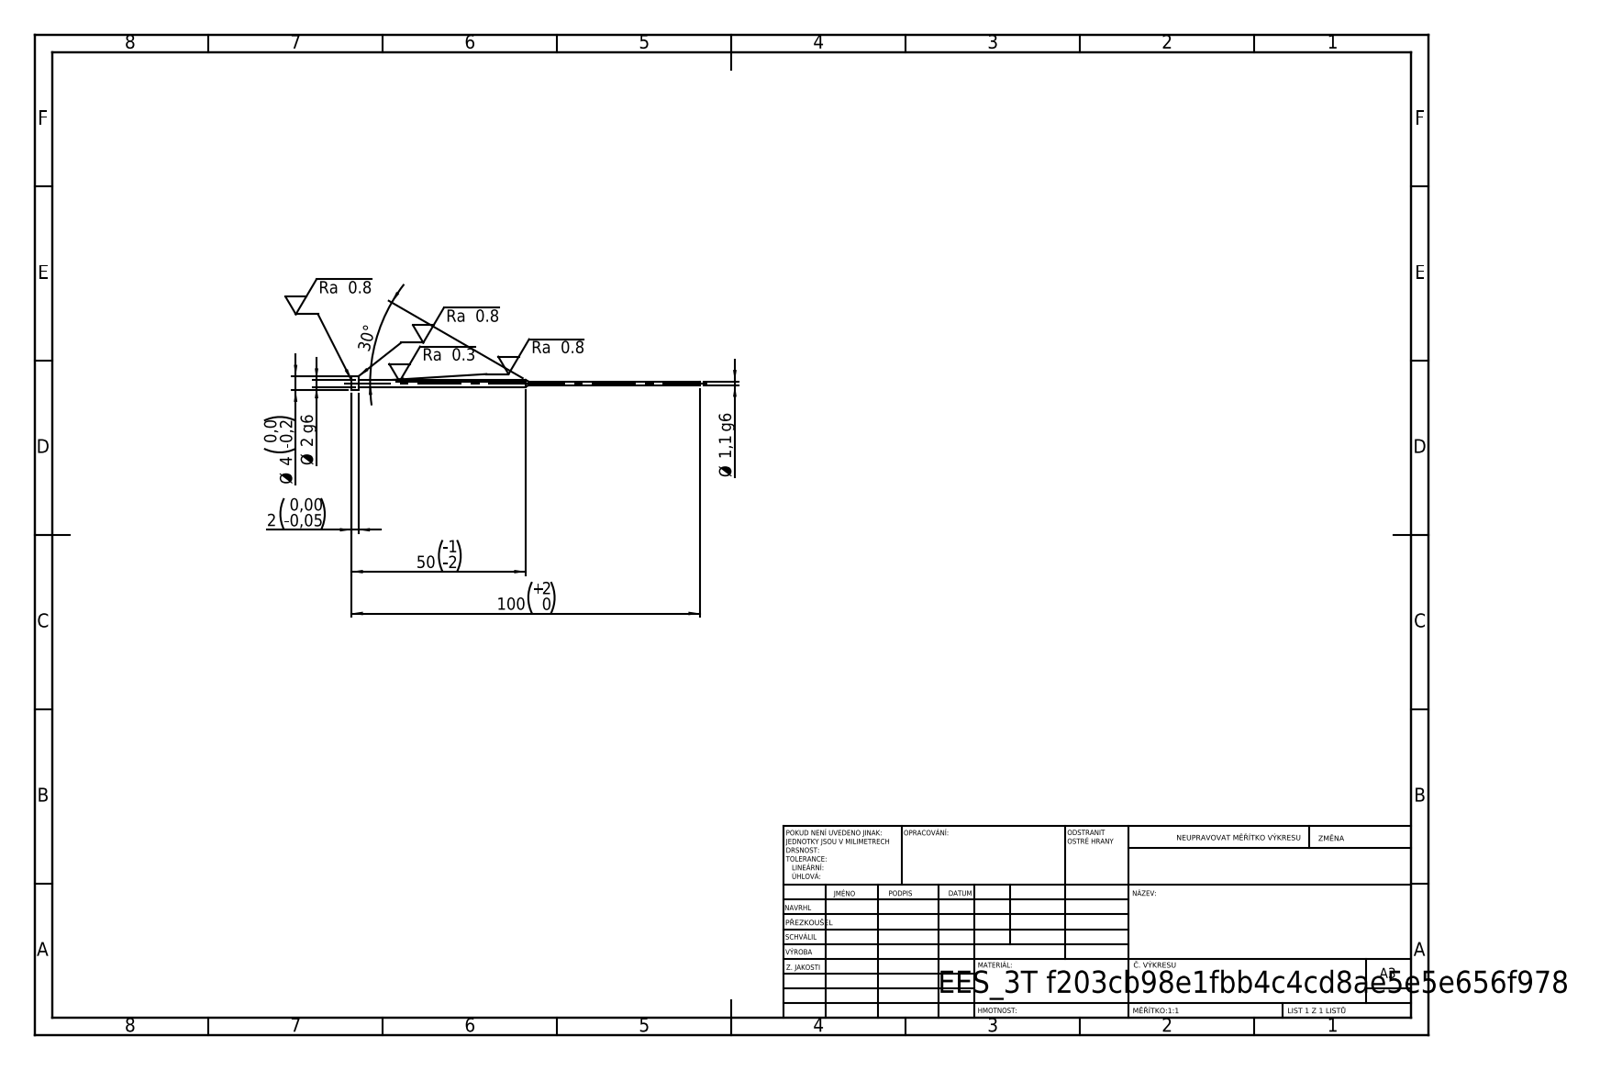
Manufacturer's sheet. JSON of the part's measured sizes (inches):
{"step_written_by": "SolidWorks 2019 (CONFIG_CONTROL_DESIGN)", "units": "inches", "bodies": {"solids": 1, "faces": 11, "planar": 3, "cylindrical": 6, "other": 2}, "overall_size": [3.937, 0.157, 0.157], "volume_in3": 0.014, "surface_area_in2": 0.812, "round_bosses_or_shafts": [[0.157, 1], [0.079, 1], [0.043, 1]], "face_to_face_distances": [0.079, 3.858, 3.937]}
